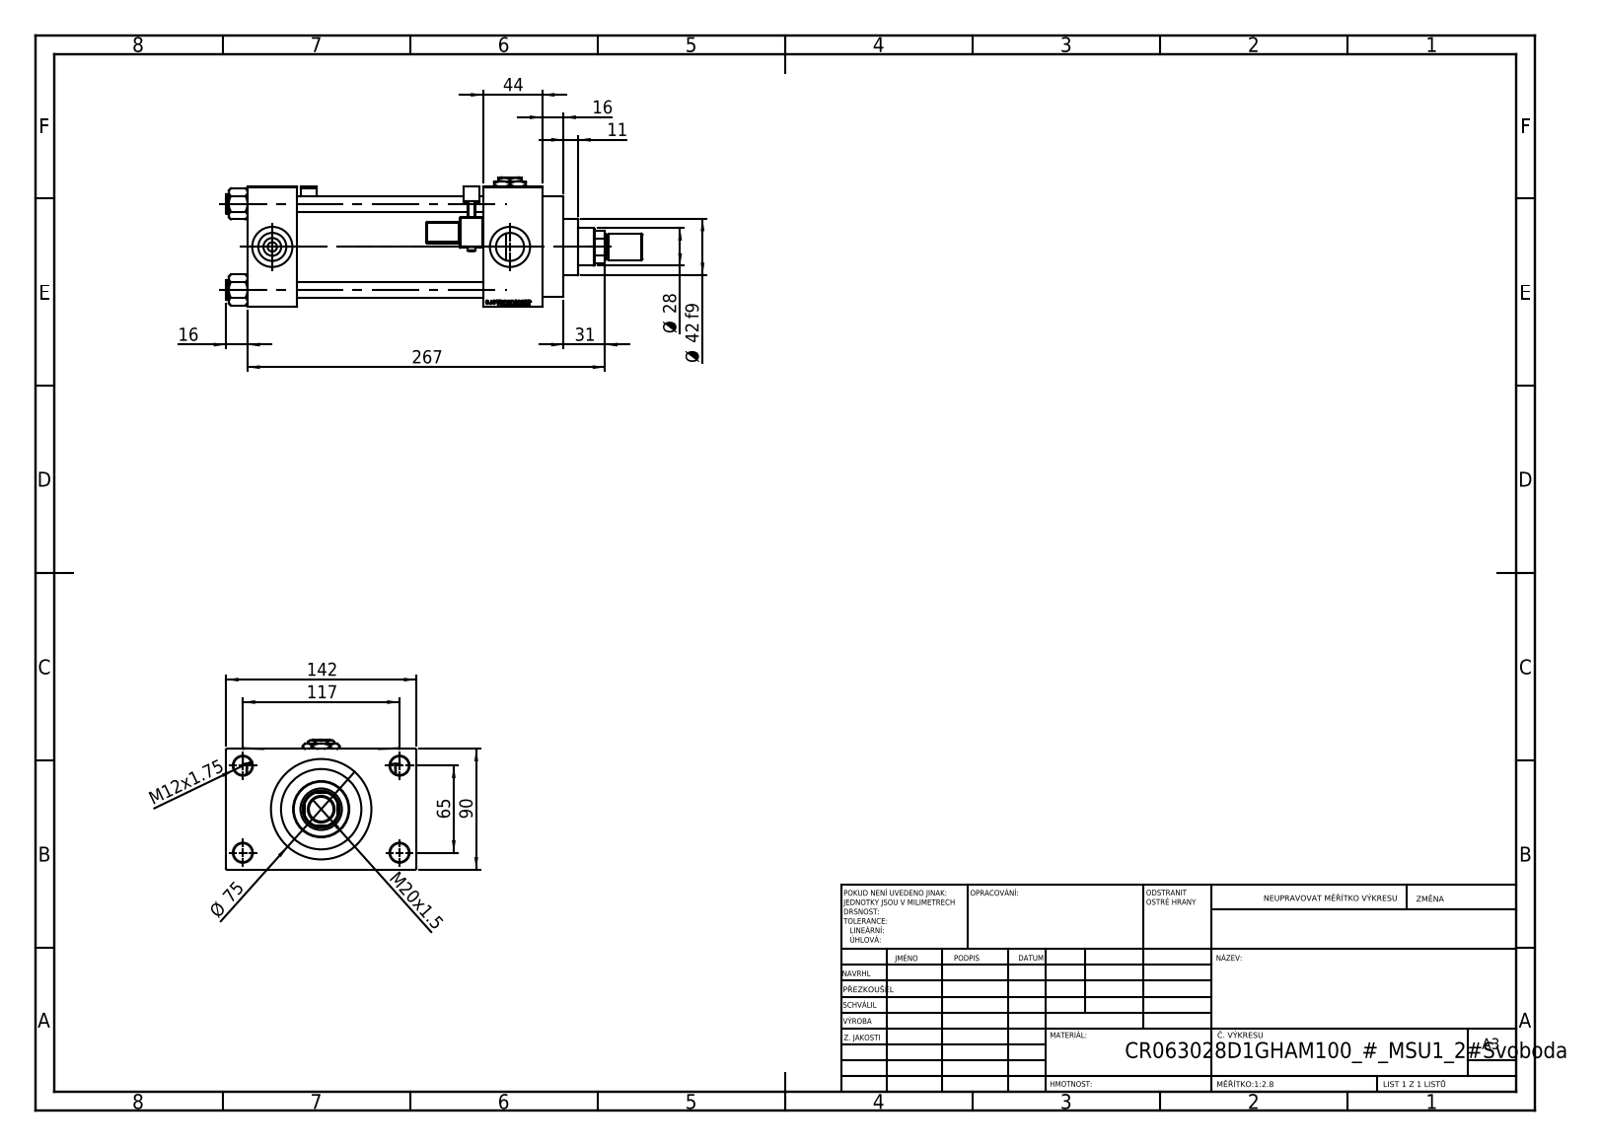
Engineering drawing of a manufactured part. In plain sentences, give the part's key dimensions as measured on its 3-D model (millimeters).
The part is named "V215CR_D_Body; V215_VC_A; V215CR_MSU; V215CR_VCP_D (+4 more)". Its 3-D file was written by "SolidWorks 2019 (CONFIG_CONTROL_DESIGN)". It is 15 solids with 1319 faces: 583 planar, 156 cylindrical and 580 other. Overall it measures 311 by 142 by 97 millimeters. Its volume is 1 278 000 cubic millimeters and its surface area 269 148 square millimeters. Round holes: 4 of diameter 12, 4 of diameter 14, 3 of diameter 20.96, 3 of diameter 30, 2 of diameter 7, 1 of diameter 18.5, 1 of diameter 28, 1 of diameter 31, 1 of diameter 50, 1 of diameter 60, 1 of diameter 63. Round bosses or shafts: 4 of diameter 15, 2 of diameter 6, 1 of diameter 75, 1 of diameter 69, 1 of diameter 42, 1 of diameter 20, 1 of diameter 18. Partial cylindrical surfaces (rounded edges, fillets, slot ends): 48 of radius 0.5, 2 of radius 1, 2 of radius 2.5, 2 of radius 4, 1 of radius 13.5. The main face-to-face distances are 90, 139, 37, 176, 220, 183, 44, 26, 116, 16. The hole center spacings are 26.35, 45.47, 64.3, 66.92, 69.81, 90.65, 111.34, 65.
